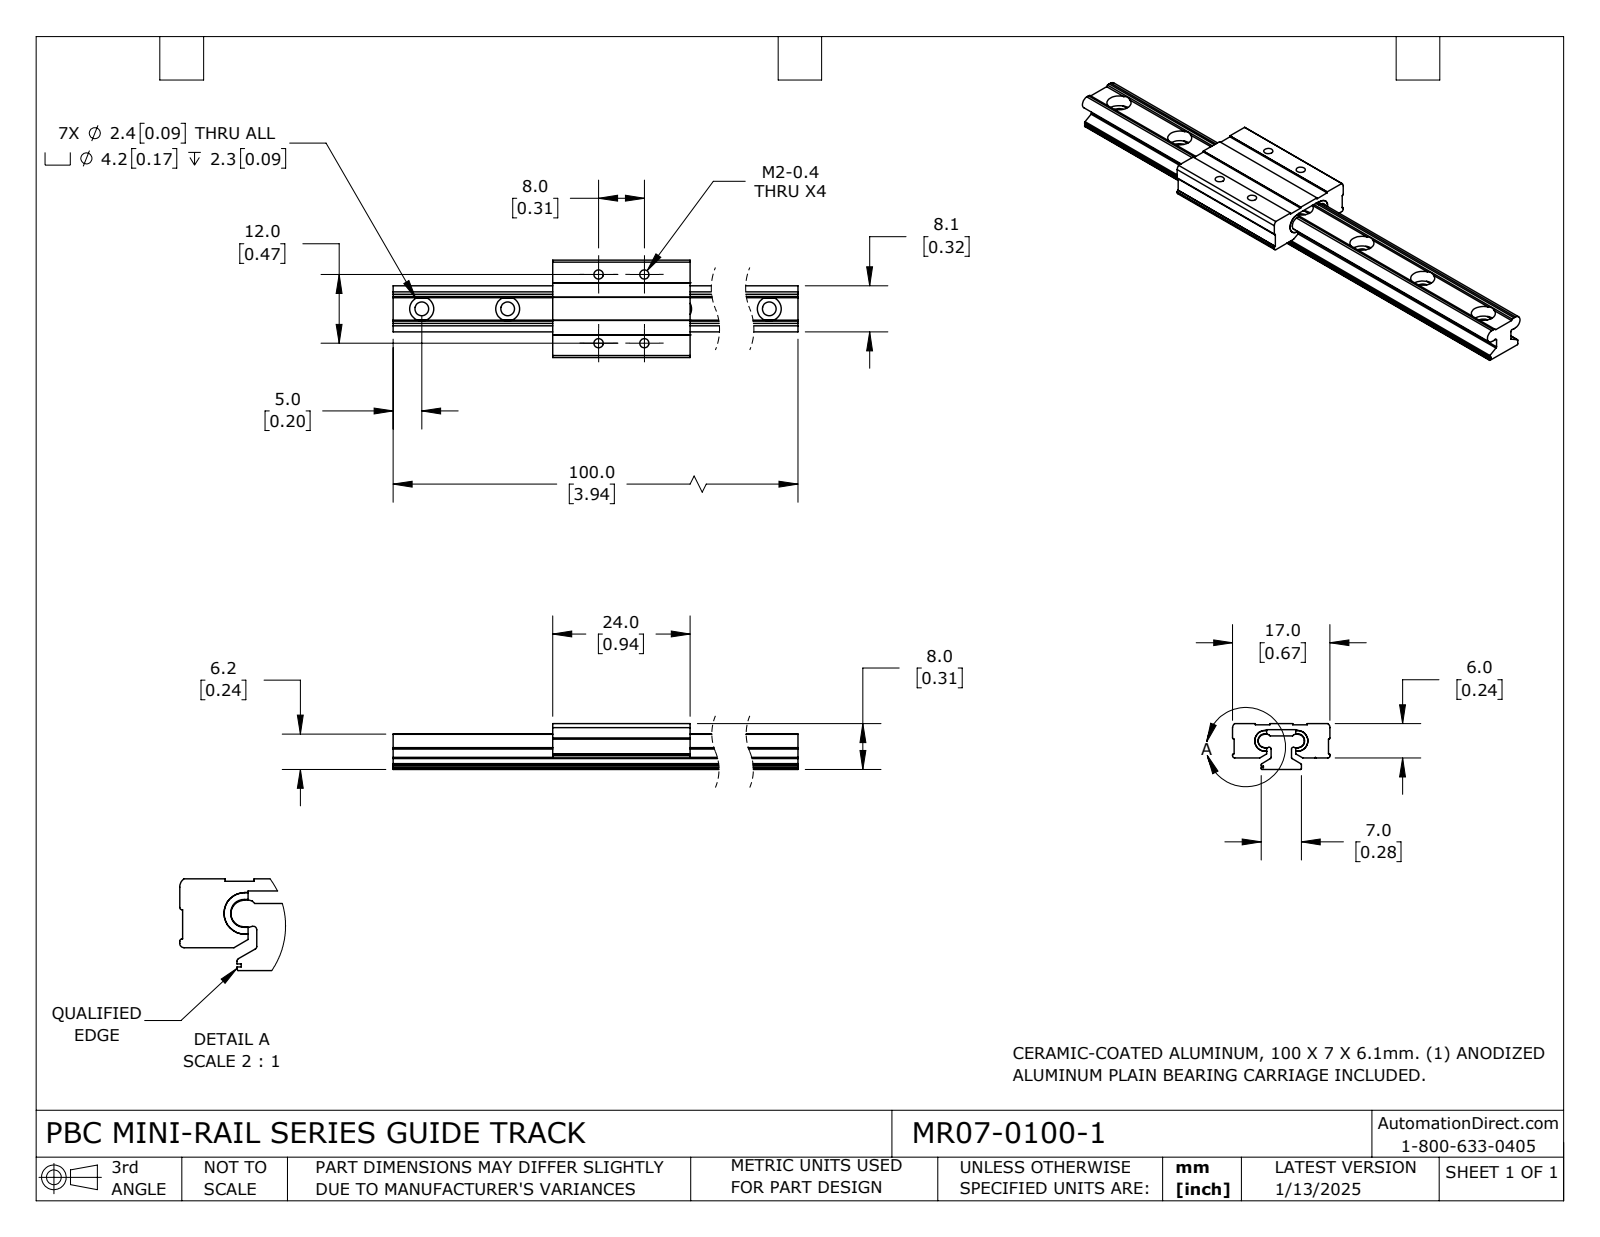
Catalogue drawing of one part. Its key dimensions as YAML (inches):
part_name: "MR07-0100-1; MR07-0100-1_RAIL; MR07-0100-1_CARRIAGE"
step_written_by: "SolidWorks 2023 (CONFIG_CONTROL_DESIGN)"
units: inches
bodies: {solids: 4, faces: 166, planar: 97, cylindrical: 69, other: 0}
overall_size: [3.937, 0.669, 0.315]
volume: 0.289
surface_area: 9.151
round_holes:
  - {diameter: 0.094, count: 7}
  - {diameter: 0.165, count: 7}
  - {diameter: 0.063, count: 4}
partial_cylinders:
  - {radius: 0.008, count: 8}
  - {radius: 0.01, count: 6}
  - {radius: 0.047, count: 4}
  - {radius: 0.012, count: 2}
  - {radius: 0.015, count: 2}
  - {radius: 0.035, count: 2}
  - {radius: 0.046, count: 2}
  - {radius: 0.071, count: 2}
face_to_face_distances: [0.231, 0.315, 0.084, 0.079, 0.152, 0.236, 0.14, 0.273, 0.194, 0.043]
hole_center_spacings: [0.591, 1.181, 1.772, 2.362, 0.239, 0.315, 0.337, 0.422]
